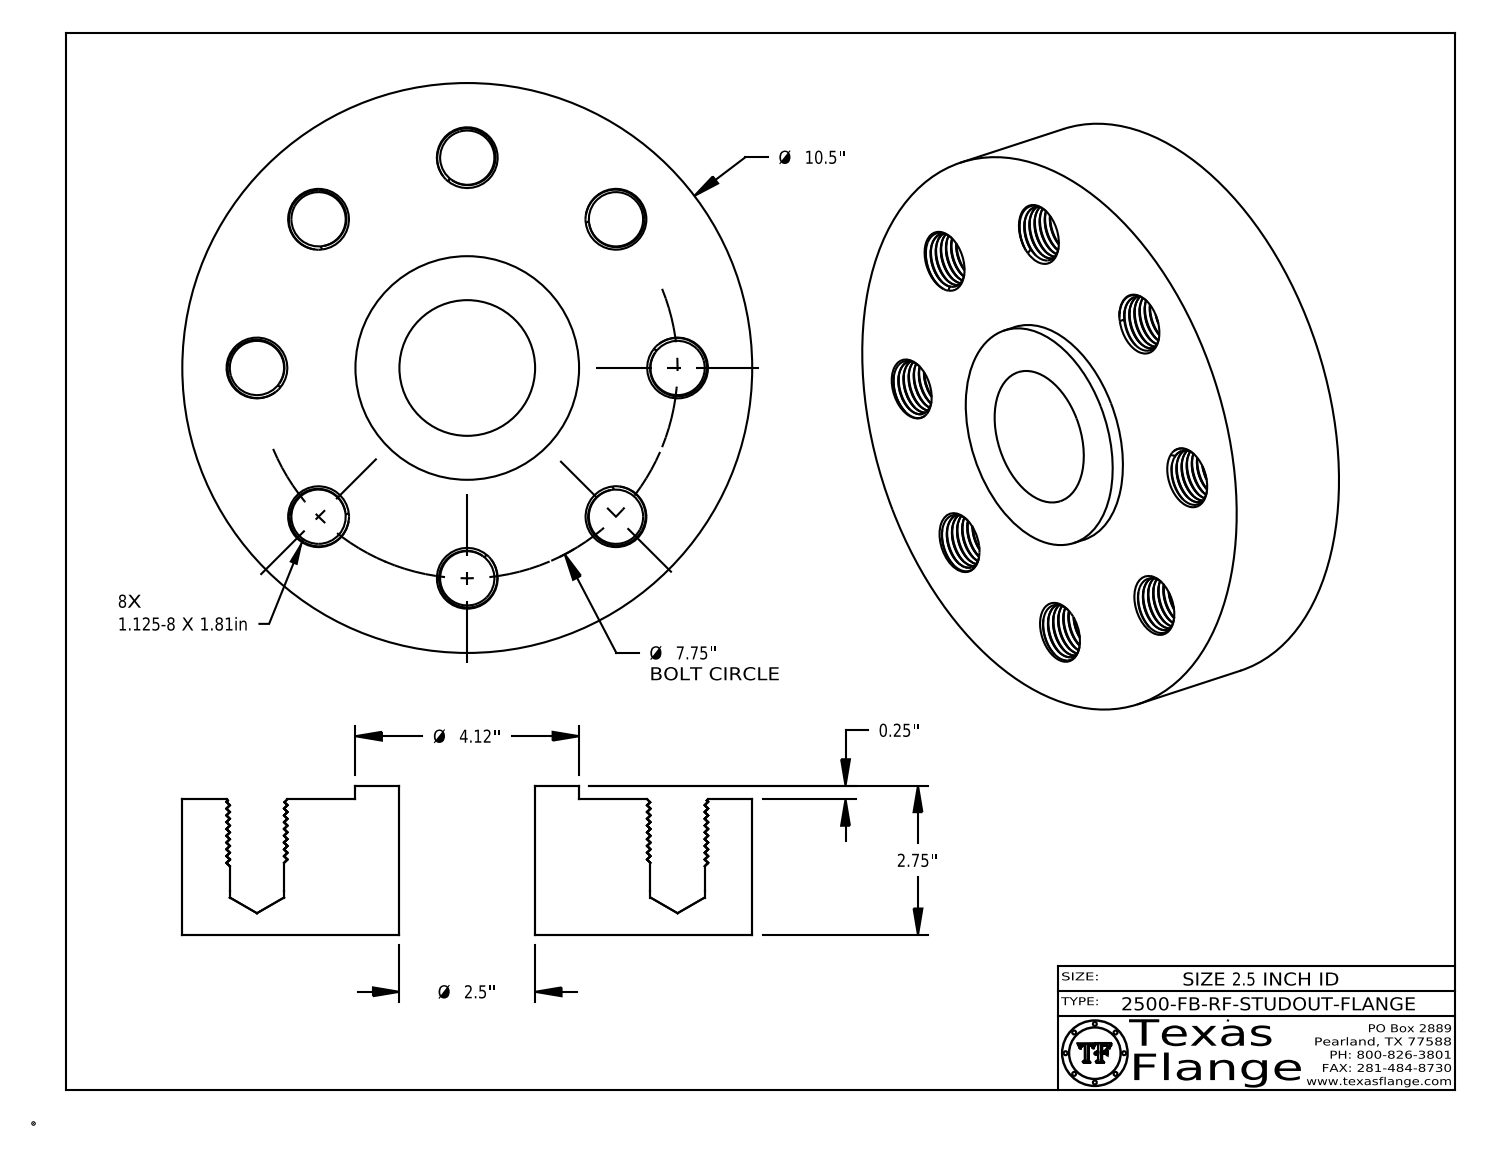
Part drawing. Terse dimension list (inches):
name: 2.5-2500-FB-RF-STUDOUT-FLANGE
written by: CATIA V5 STEP AP214 (AUTOMOTIVE_DESIGN)
unit: in
bodies: 1 solid, 938 faces (368 planar, 202 cylindrical, 368 other)
size: 10.5 × 10.5 × 2.75
volume: 193.4 in³; area: 331 in²
holes: 8× ⌀1, 1× ⌀2.5
bosses: 8× ⌀0.061, 1× ⌀10.5, 1× ⌀4.12, 1× ⌀0.788
face distances: 2.5, 0.25, 2.75, 0.015, 2.735, 2.485, 0.298, 0.292, 0.054, 0.248
hole spacings: 2.966, 3.875, 5.48, 7.16, 7.75
